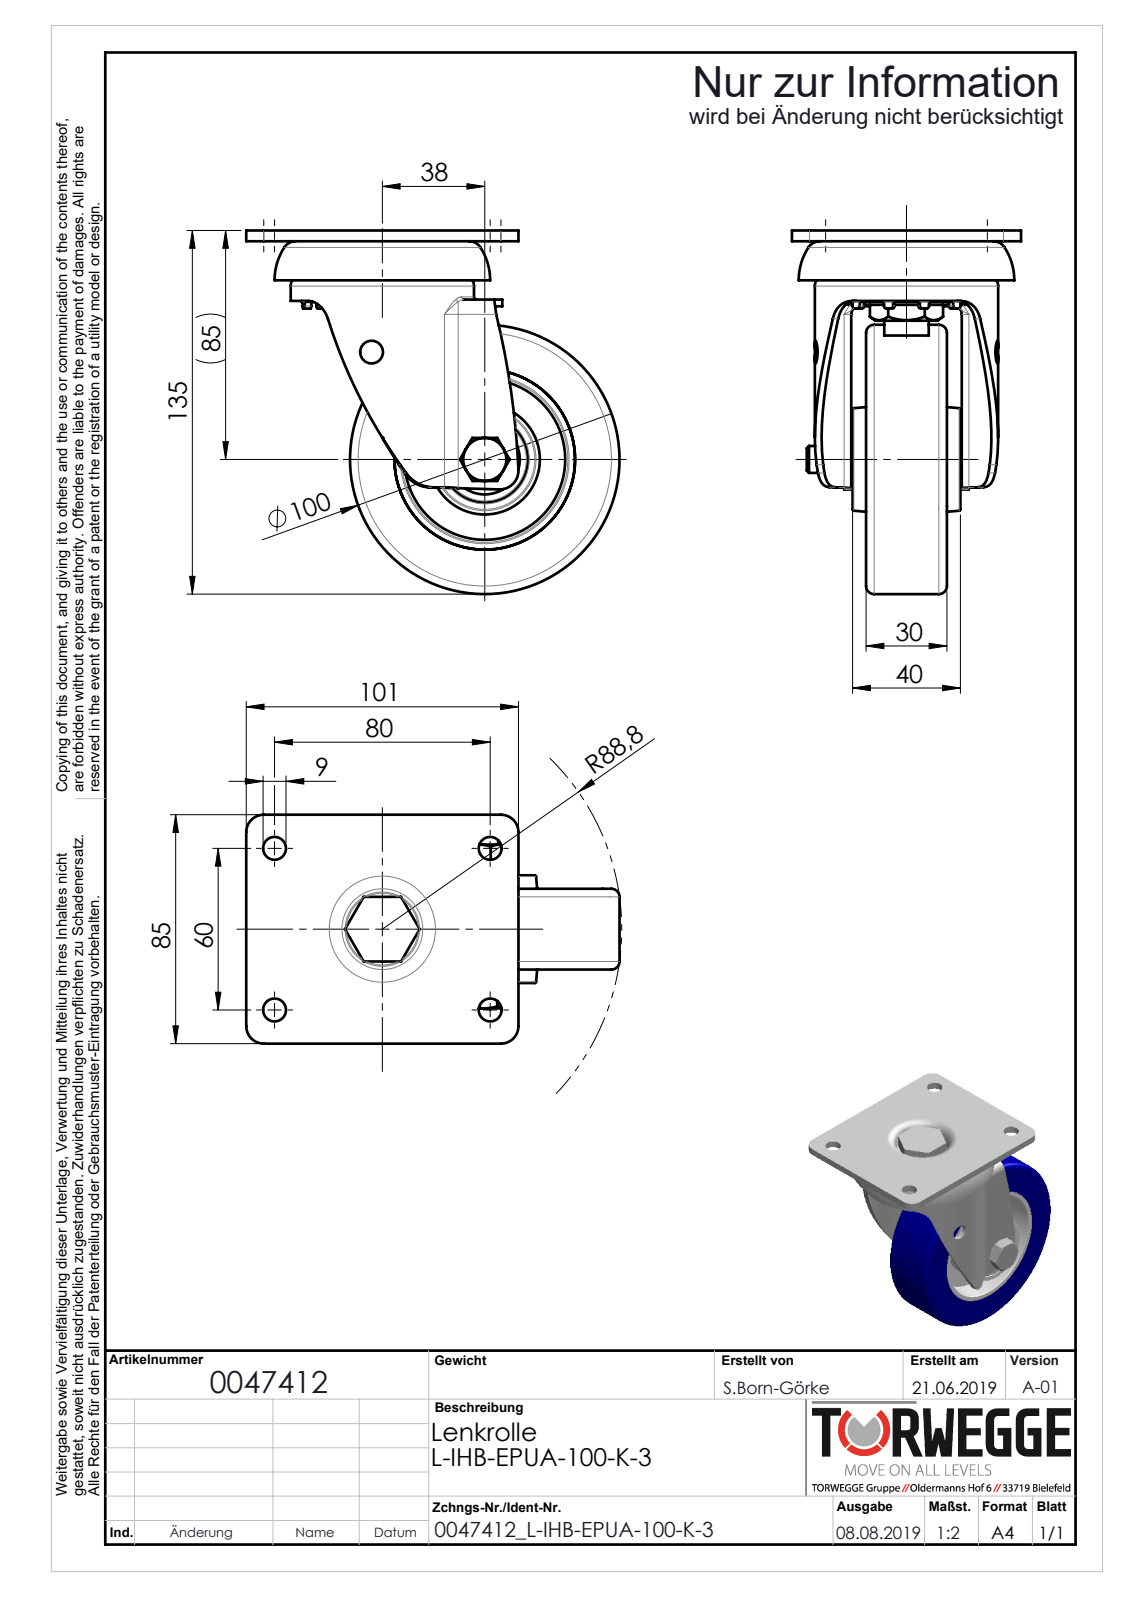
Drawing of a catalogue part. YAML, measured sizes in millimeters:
part_name: "0047412_L-IHB-EPUA-100-K-3_(A-01)"
step_written_by: "SolidWorks 2018 (AUTOMOTIVE_DESIGN)"
units: millimeters
bodies: {solids: 0, faces: 415, planar: 153, cylindrical: 133, other: 129}
overall_size: [138.5, 135, 85]
round_holes:
  - {diameter: 8.5, count: 6}
  - {diameter: 10, count: 1}
  - {diameter: 10.2, count: 1}
  - {diameter: 10.5, count: 1}
  - {diameter: 12, count: 1}
  - {diameter: 26, count: 1}
  - {diameter: 67, count: 1}
round_bosses_or_shafts:
  - {diameter: 100, count: 1}
  - {diameter: 68, count: 1}
  - {diameter: 18, count: 1}
  - {diameter: 16.5, count: 1}
  - {diameter: 16, count: 1}
partial_cylinders:
  - {radius: 1, count: 22}
  - {radius: 6.5, count: 4}
  - {radius: 3, count: 2}
  - {radius: 5.5, count: 2}
  - {radius: 7.5, count: 2}
  - {radius: 10, count: 2}
  - {radius: 7, count: 1}
  - {radius: 27.5, count: 1}
face_to_face_distances: [4, 18.5, 30, 19.5, 8, 11.5, 26.5, 2.5, 38, 24]
hole_center_spacings: [60, 80, 100, 57.9]
